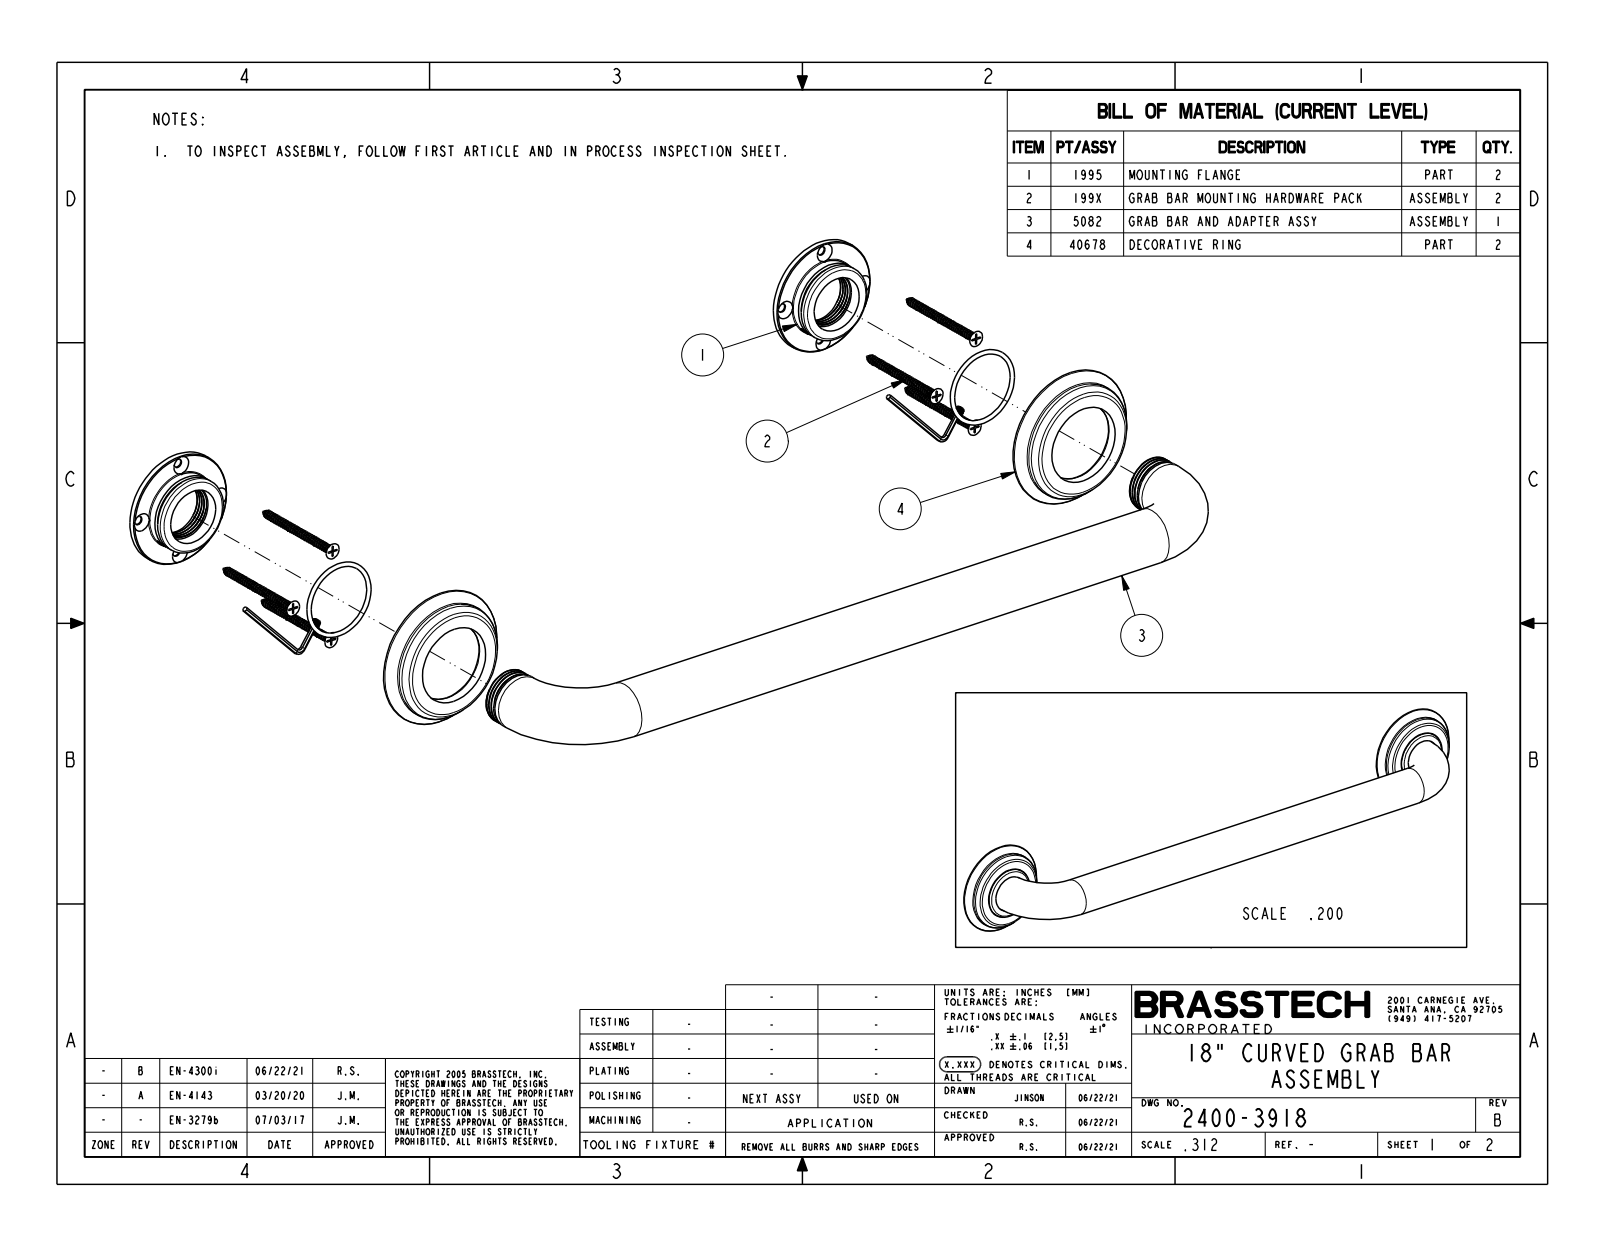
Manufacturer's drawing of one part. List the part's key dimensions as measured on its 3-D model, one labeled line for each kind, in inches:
Part name (STEP PRODUCT): 2400-3918
STEP written by: CREO PARAMETRIC BY PTC INC, 2018400 (CONFIG_CONTROL_DESIGN)
Units: inches
Bodies: 1 solid, 44 faces (6 planar, 6 cylindrical, 32 other)
Overall size (bounding box): 21.154 × 3.154 × 2.75
Volume: 30.86 in³ · Surface area: 111.5 in²
Round bosses / shafts (diameter × count): ⌀1.75 ×2, ⌀1.25 ×1
Main face-to-face distances: 0.525, 0.6, 0.075
